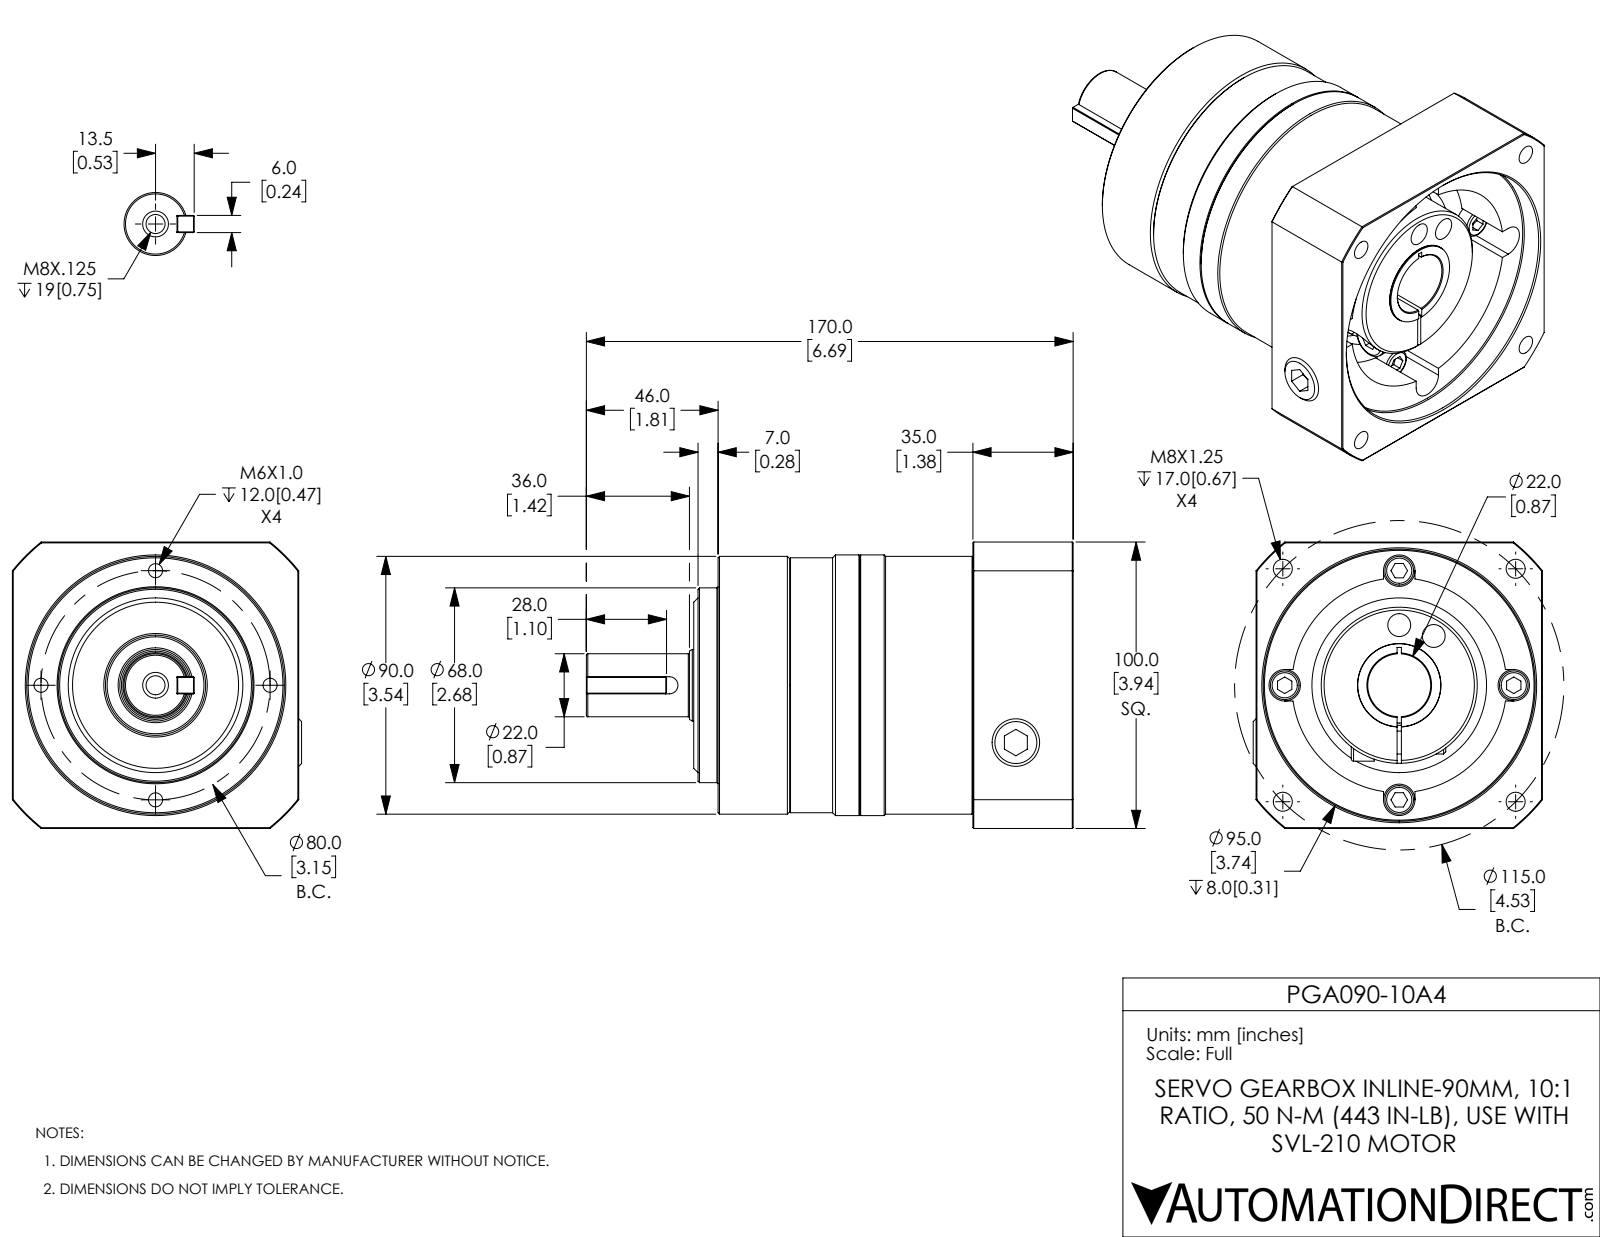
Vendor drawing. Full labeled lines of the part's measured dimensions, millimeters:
Part name (STEP PRODUCT): PGA090-10A4
STEP written by: SolidWorks 2019 (CONFIG_CONTROL_DESIGN)
Units: millimetres
Bodies: 1 solid, 328 faces (127 planar, 91 cylindrical, 110 other)
Overall size (bounding box): 170 × 101 × 100
Volume: 800 300 mm³ · Surface area: 89 810 mm²
Round holes (diameter × count): ⌀6.7 ×5, ⌀4.9 ×4, ⌀11 ×4, ⌀8 ×2, ⌀8.8 ×1, ⌀14.2 ×1, ⌀22 ×1, ⌀61 ×1, ⌀75 ×1, ⌀95 ×1
Round bosses / shafts (diameter × count): ⌀10 ×4, ⌀91 ×1, ⌀90 ×1, ⌀89 ×1, ⌀68 ×1, ⌀54.5 ×1, ⌀29 ×1, ⌀28 ×1
Partial cylindrical surfaces — rounded edges, fillets, slot ends (radius × count): R3 ×1, R3.3 ×1, R7 ×1, R64 ×1
Main face-to-face distances: 100, 7, 96, 89, 8, 35, 28, 124, 27, 20
Hole centre spacings: 40.7, 90.3, 40, 56.6, 57.5, 81.3, 21, 45.2
